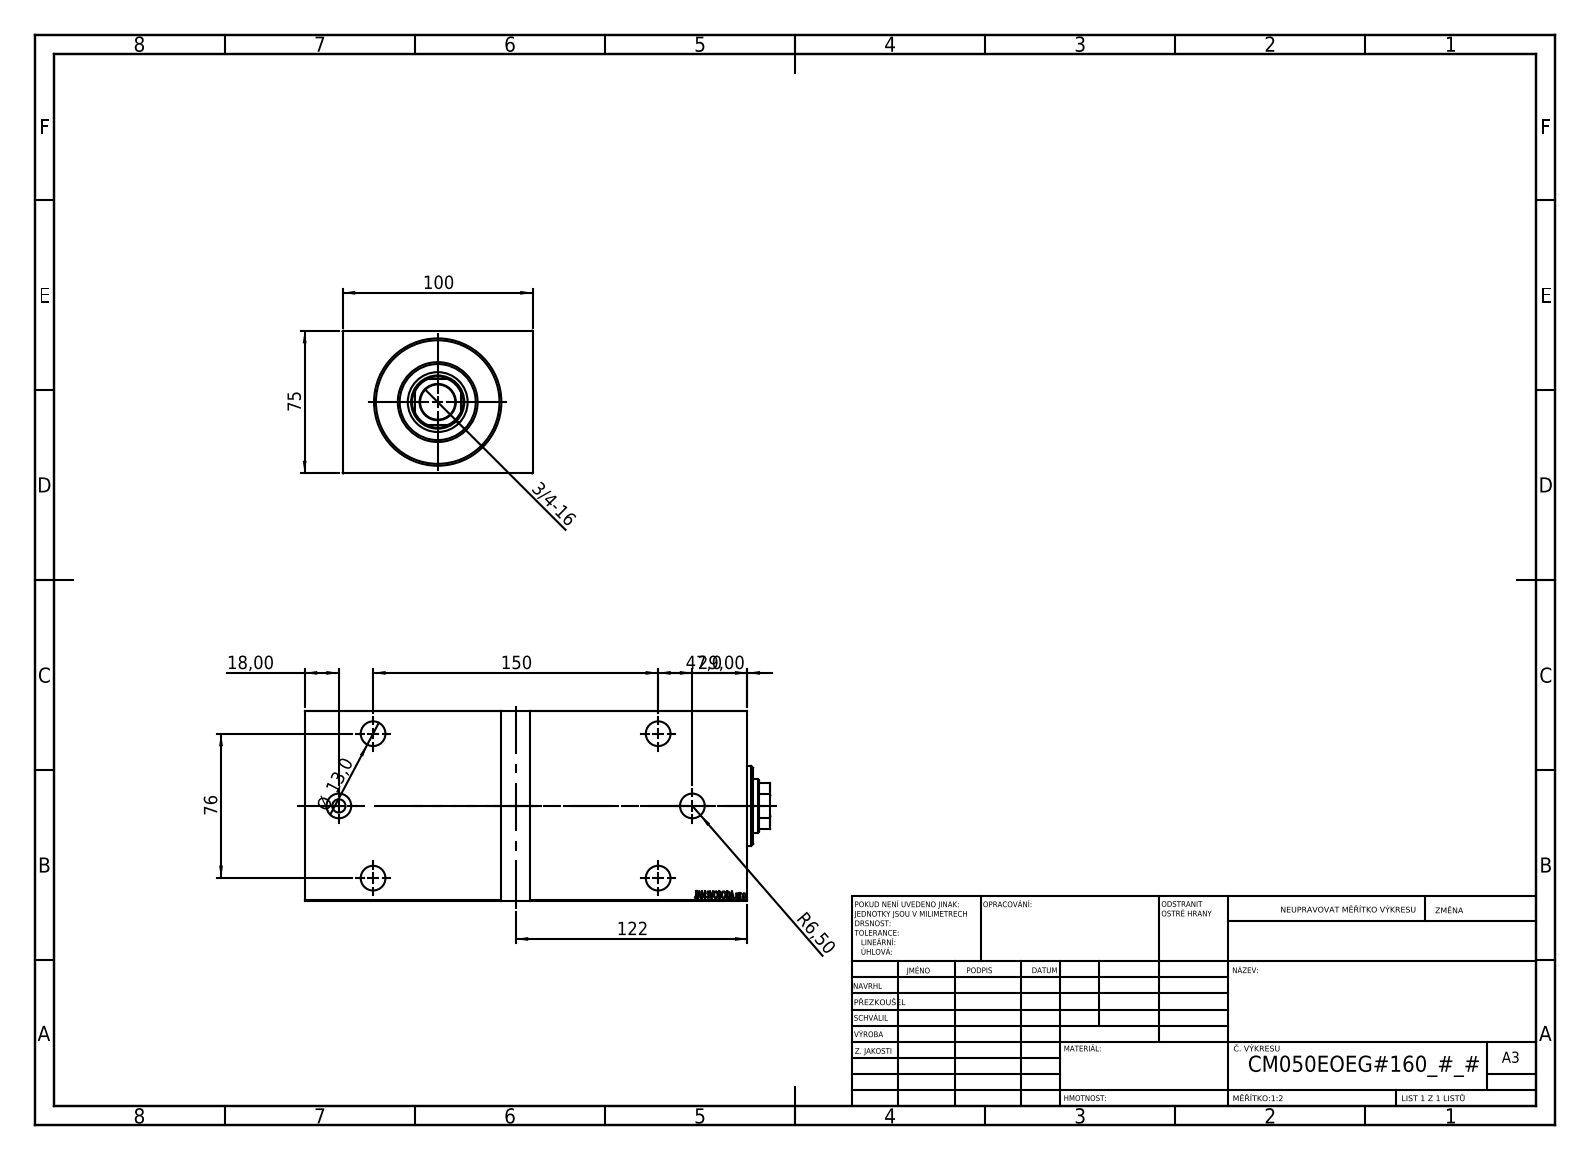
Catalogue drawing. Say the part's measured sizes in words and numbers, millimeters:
The part is named "V450CM_E_VCP; V450CM_VC_B; V450CM_E_Body". Its 3-D file was written by "SolidWorks 2019 (CONFIG_CONTROL_DESIGN)". It is 3 solids with 849 faces: 409 planar, 46 cylindrical and 394 other. Overall it measures 245 by 100 by 75 millimeters. Its volume is 1 481 000 cubic millimeters and its surface area 184 155 square millimeters. Round holes: 6 of diameter 13, 4 of diameter 19, 1 of diameter 18.5, 1 of diameter 28, 1 of diameter 31.5, 1 of diameter 50, 1 of diameter 65. Round bosses or shafts: 1 of diameter 52, 1 of diameter 42, 1 of diameter 7. Partial cylindrical surfaces (rounded edges, fillets, slot ends): 1 of radius 13.5. The main face-to-face distances are 75, 100, 233, 5, 14, 219, 228, 214, 216.4, 202.4. The hole center spacings are 42.05, 172.24, 76, 150, 168.15, 186.
